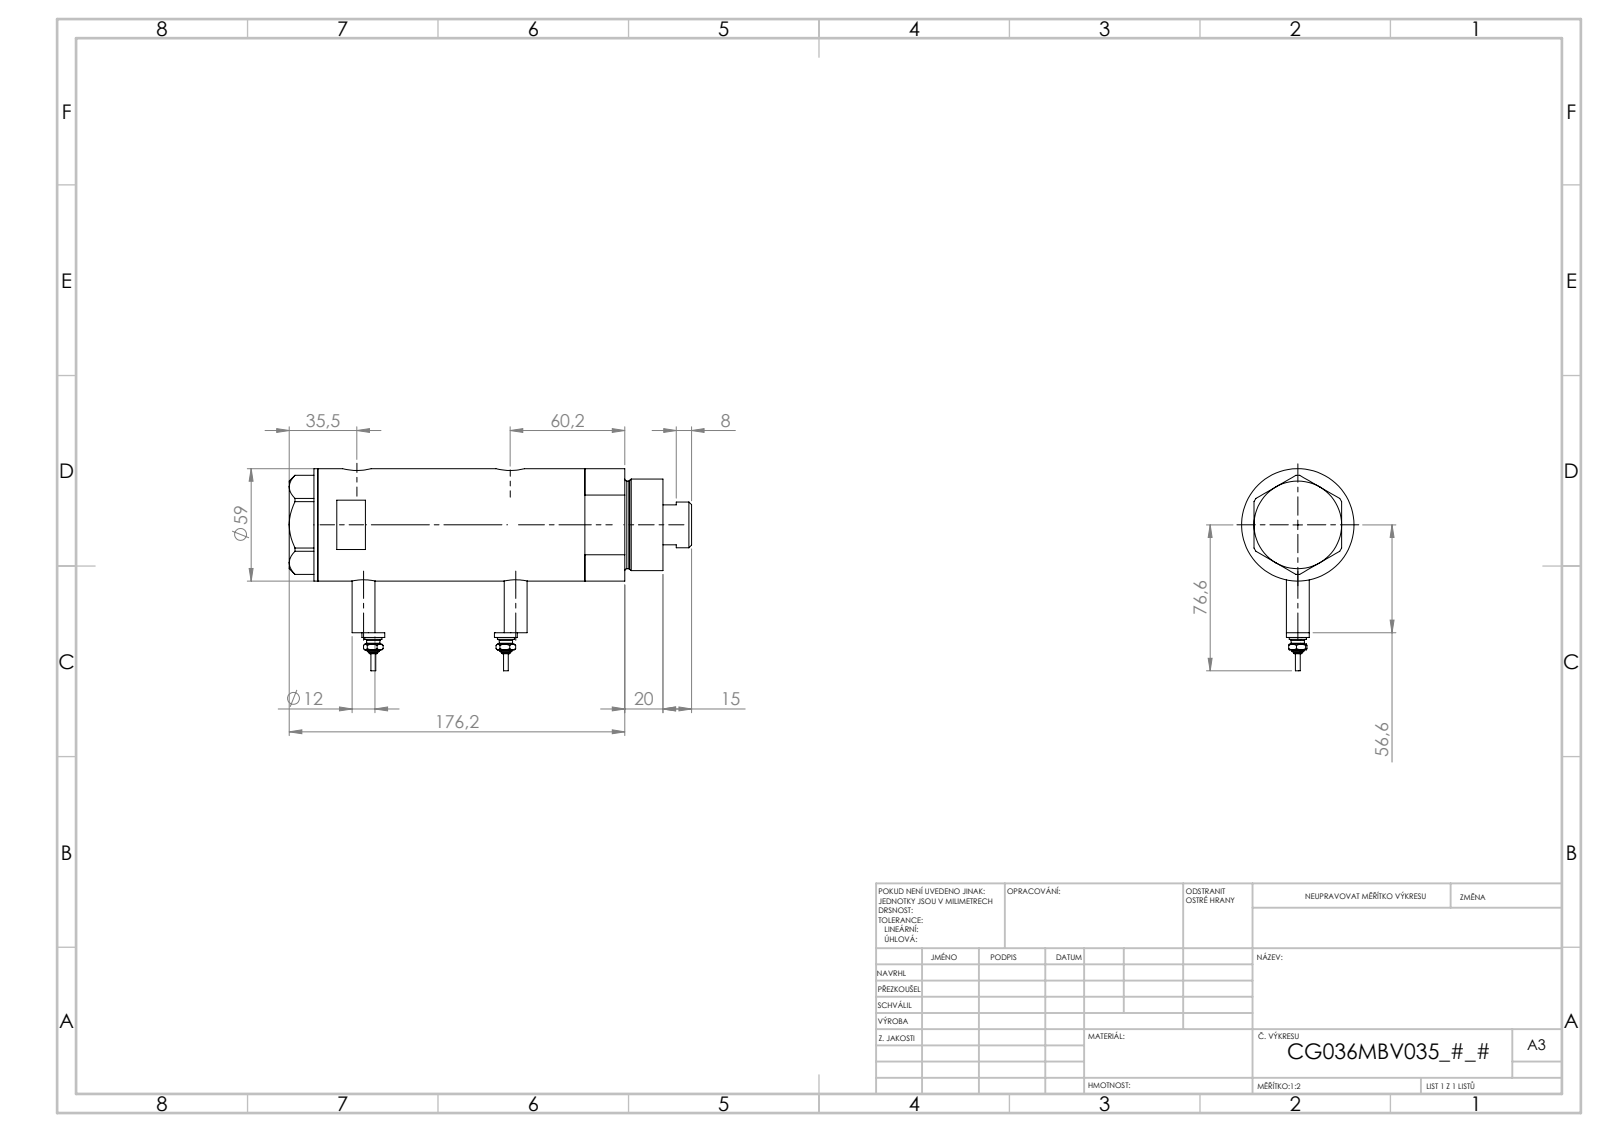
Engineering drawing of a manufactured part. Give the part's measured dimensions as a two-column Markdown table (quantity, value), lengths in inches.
| quantity | value |
| --- | --- |
| part name | V270CG_VC; V270CG_BACK; V270CG_SWITCH; V270CG_MIDDLE (+1 more) |
| STEP written by | SolidWorks 2019 (CONFIG_CONTROL_DESIGN) |
| units | inches |
| bodies | 6 solids, 232 faces (81 planar, 77 cylindrical, 74 other) |
| overall size | 7.812 × 3.594 × 2.323 |
| volume | 27.54 in³ |
| surface area | 150.4 in² |
| round holes (diameter × count) | 0.197 × 2, 0.383 × 2, 0.492 × 2, 0.591 × 2, 0.335 × 1, 0.984 × 1, 1.043 × 1, 1.417 × 1, 1.575 × 1, 2.047 × 1 |
| round bosses / shafts (diameter × count) | 0.472 × 3, 0.354 × 2, 0.276 × 2, 0.171 × 2, 0.094 × 2, 2.323 × 1, 1.89 × 1, 1.811 × 1 |
| main face-to-face distances | 3.635, 0.925, 2.71, 0.591, 1.516, 4.226, 7.221, 6.631, 5.706, 2.995 |
| hole center spacings | 0.114, 0.138, 2.644, 2.758, 2.781, 2.896, 0.114, 0.115 |
